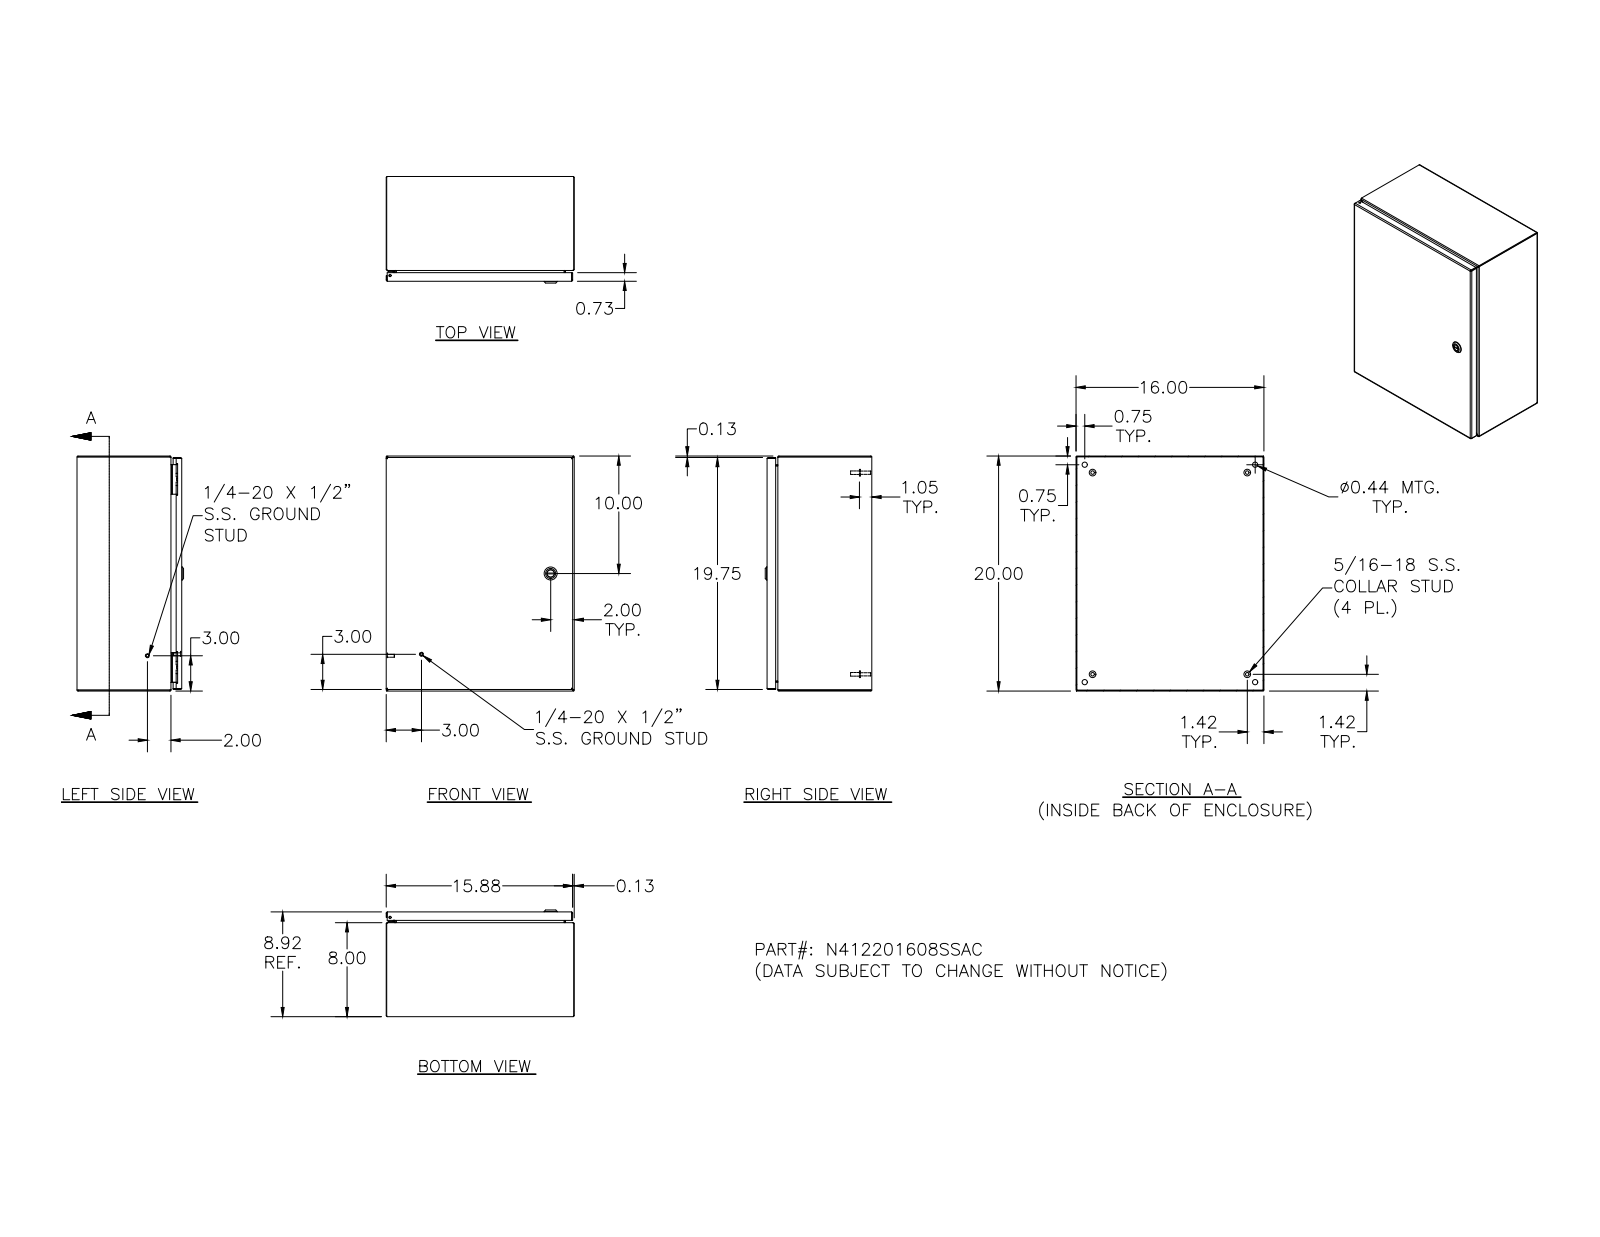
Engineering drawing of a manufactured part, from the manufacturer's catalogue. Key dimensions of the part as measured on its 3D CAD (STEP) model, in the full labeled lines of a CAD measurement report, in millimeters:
Part name (STEP PRODUCT): N412201608SSAC; N412201608SSACBKP; 388151; N4122016SSACLID (+8 more)
STEP written by: Autodesk Inventor 2011 (AUTOMOTIVE_DESIGN)
Units: millimetres
Bodies: 34 solids, 1364 faces (523 planar, 497 cylindrical, 344 other)
Overall size (bounding box): 508 × 406.4 × 230.5
Volume: 1 657 000 mm³ · Surface area: 1 774 000 mm²
Round holes (diameter × count): ⌀4.8 ×5, ⌀2.4 ×4, ⌀3.9 ×4, ⌀4.2 ×4, ⌀4.4 ×4, ⌀11.1 ×4, ⌀4 ×2, ⌀4.7 ×1, ⌀5 ×1, ⌀8 ×1, ⌀10 ×1, ⌀10.2 ×1
Round bosses / shafts (diameter × count): ⌀6.4 ×10, ⌀14.3 ×4, ⌀9.1 ×4, ⌀8.1 ×4, ⌀7.6 ×4, ⌀7 ×4, ⌀6.5 ×4, ⌀4.2 ×4
Partial cylindrical surfaces — rounded edges, fillets, slot ends (radius × count): R1.3 ×26, R0.4 ×18, R0.4 ×16, R2.3 ×16, R0.8 ×14, R3.2 ×14, R0.5 ×9, R0.8 ×8
Main face-to-face distances: 1.9, 224.6, 404.5, 222.7, 226.5, 506.1, 406.4, 402.6, 508, 504.2
Hole centre spacings: 406.4, 0.4, 16.8, 406.6, 0.5, 12.7, 16.5, 16.6
